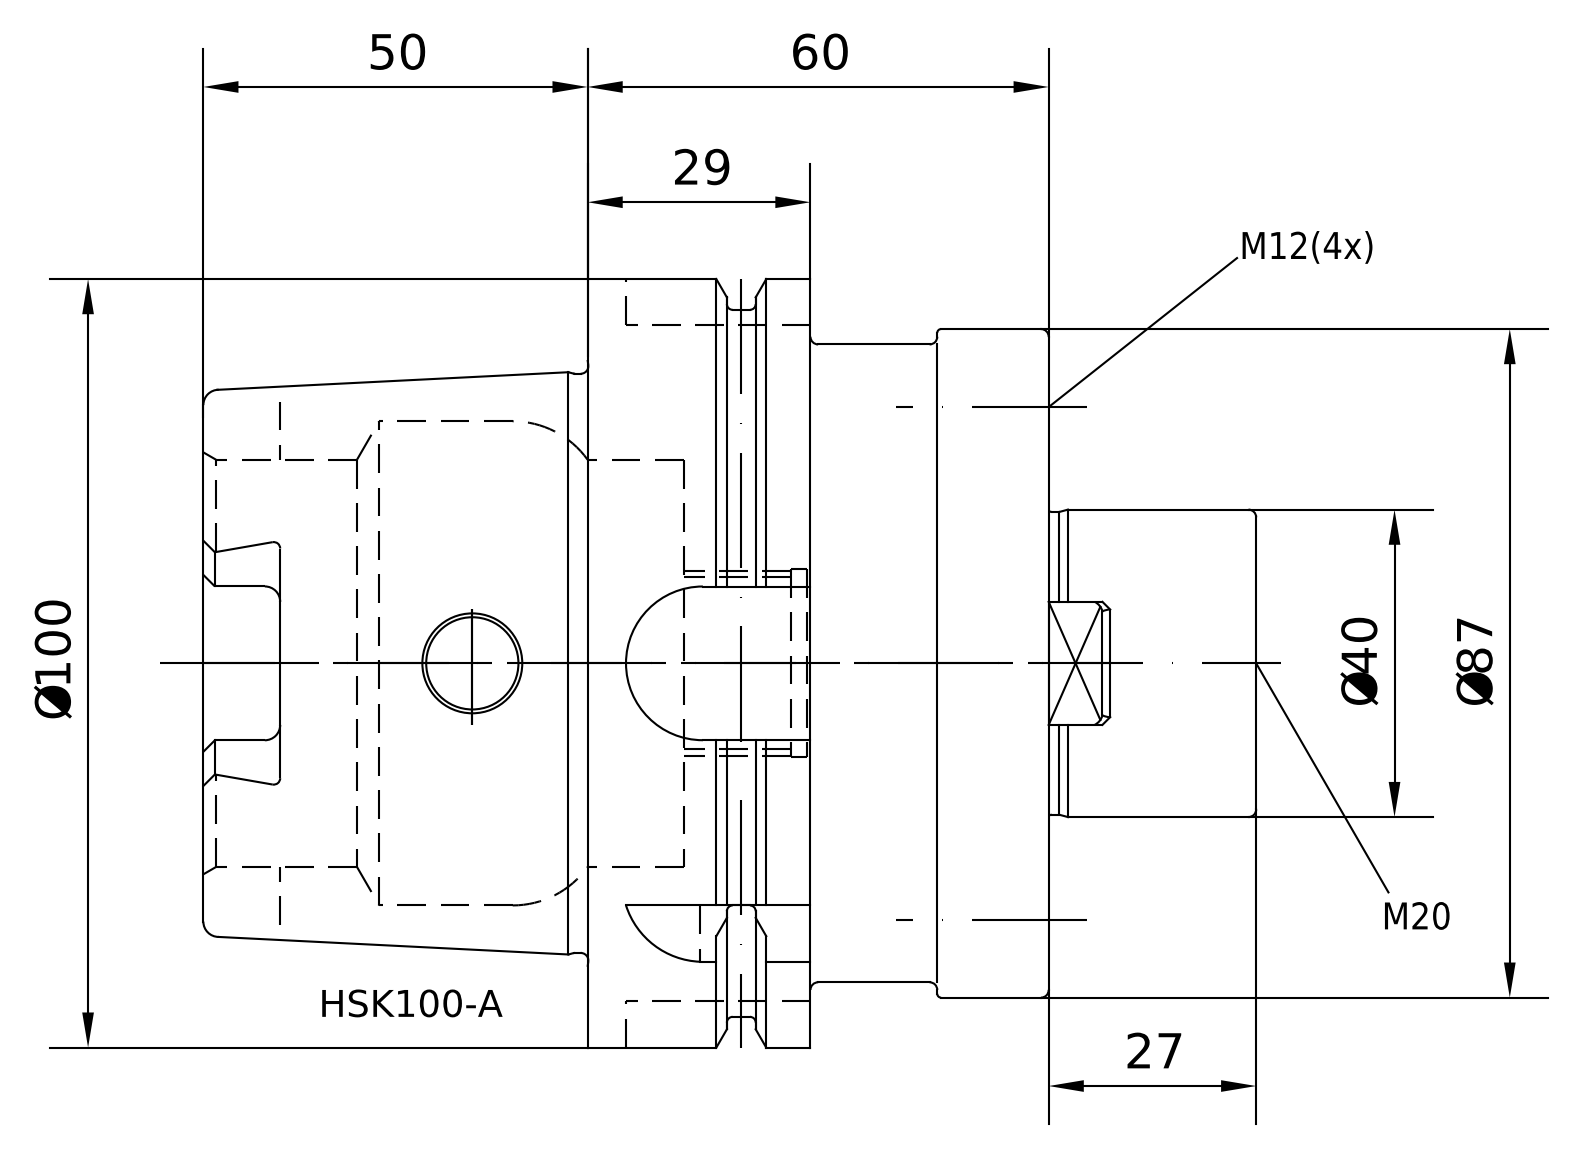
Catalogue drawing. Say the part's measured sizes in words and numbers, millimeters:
The part is named "A100-050-40". Its 3-D file was written by "PRO/ENGINEER BY PARAMETRIC TECHNOLOGY CORPORATION, 2010430 (CONFIG_CONTROL_DESIGN)". It is 1 solid with 226 faces: 66 planar, 73 cylindrical and 87 other. Overall it measures 137 by 100 by 100 millimeters. Its volume is 447 970 cubic millimeters and its surface area 74 658 square millimeters. Round holes: 5 of diameter 12, 4 of diameter 10.2, 1 of diameter 10, 1 of diameter 17.5, 1 of diameter 20, 1 of diameter 22.5, 1 of diameter 24, 1 of diameter 24.32, 1 of diameter 24.5, 1 of diameter 53, 1 of diameter 63. Round bosses or shafts: 1 of diameter 100, 1 of diameter 92, 1 of diameter 87, 1 of diameter 83, 1 of diameter 75.36, 1 of diameter 40. Partial cylindrical surfaces (rounded edges, fillets, slot ends): 6 of radius 2, 4 of radius 5, 1 of radius 8, 1 of radius 10, 1 of radius 11. The main face-to-face distances are 60, 29, 31, 12.5, 47.5, 16.5, 79, 16, 87, 74.5. The hole center spacings are 33.35, 47.16, 66.69.
